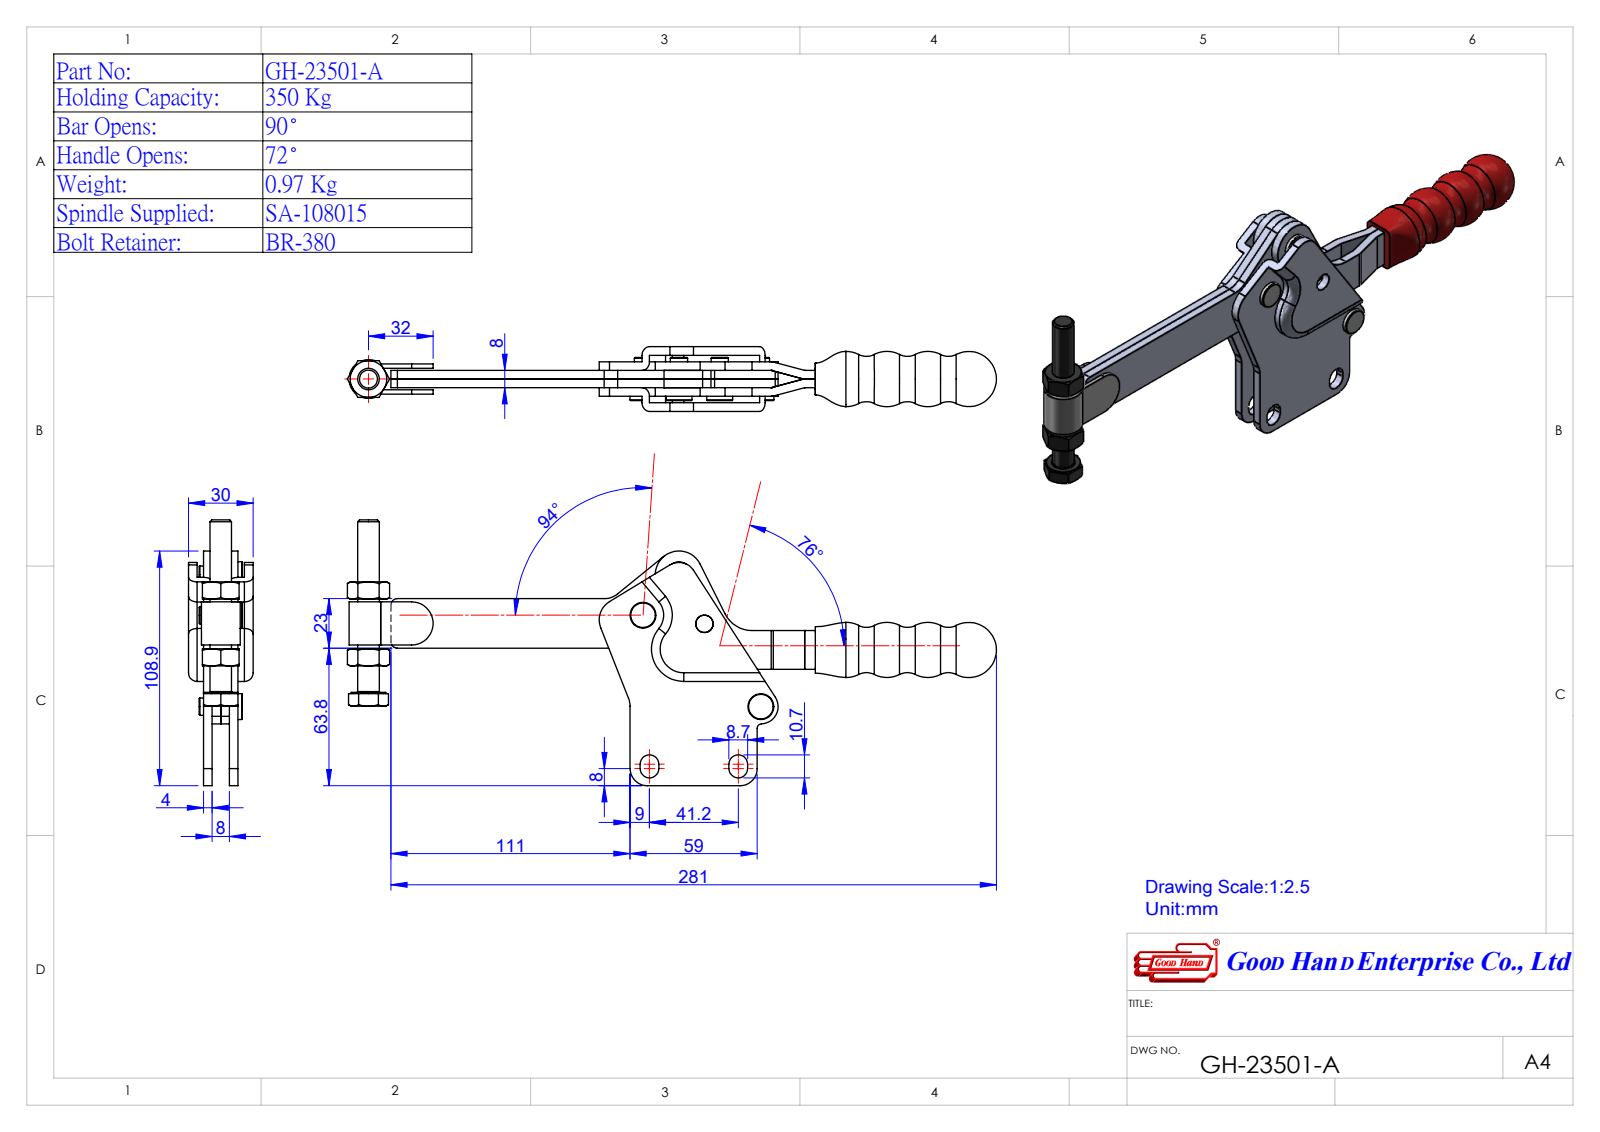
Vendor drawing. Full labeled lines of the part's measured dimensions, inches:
Part name (STEP PRODUCT): Group2^GH-23501-A(簡化)-1; Group1^GH-23501-A(簡化)-1; Group1^GH-23501-A(簡化); Group3^GH-23501-A(簡化)-1 (+2 more)
STEP written by: SolidWorks 2016 (AUTOMOTIVE_DESIGN)
Units: inches
Bodies: 5 solids, 341 faces (128 planar, 141 cylindrical, 72 other)
Overall size (bounding box): 11.796 × 4.923 × 1.496
Volume: 9.36 in³ · Surface area: 101.3 in²
Round holes (diameter × count): ⌀0.236 ×4, ⌀0.315 ×2
Round bosses / shafts (diameter × count): ⌀0.472 ×4, ⌀0.315 ×4, ⌀0.63 ×1, ⌀0.394 ×1
Partial cylindrical surfaces — rounded edges, fillets, slot ends (radius × count): R0.039 ×4, R0.079 ×4, R0.158 ×4, R0.171 ×4, R0.315 ×4, R0.394 ×3, R0.433 ×2, R0.551 ×2
Main face-to-face distances: 0.157, 0.315, 0.472, 0.571, 0.276, 0.748, 0.63, 0.729, 0.414, 0.256
Hole centre spacings: 1.011, 1.83, 0.489, 0.489, 0.99, 1.133, 1.133, 1.341
